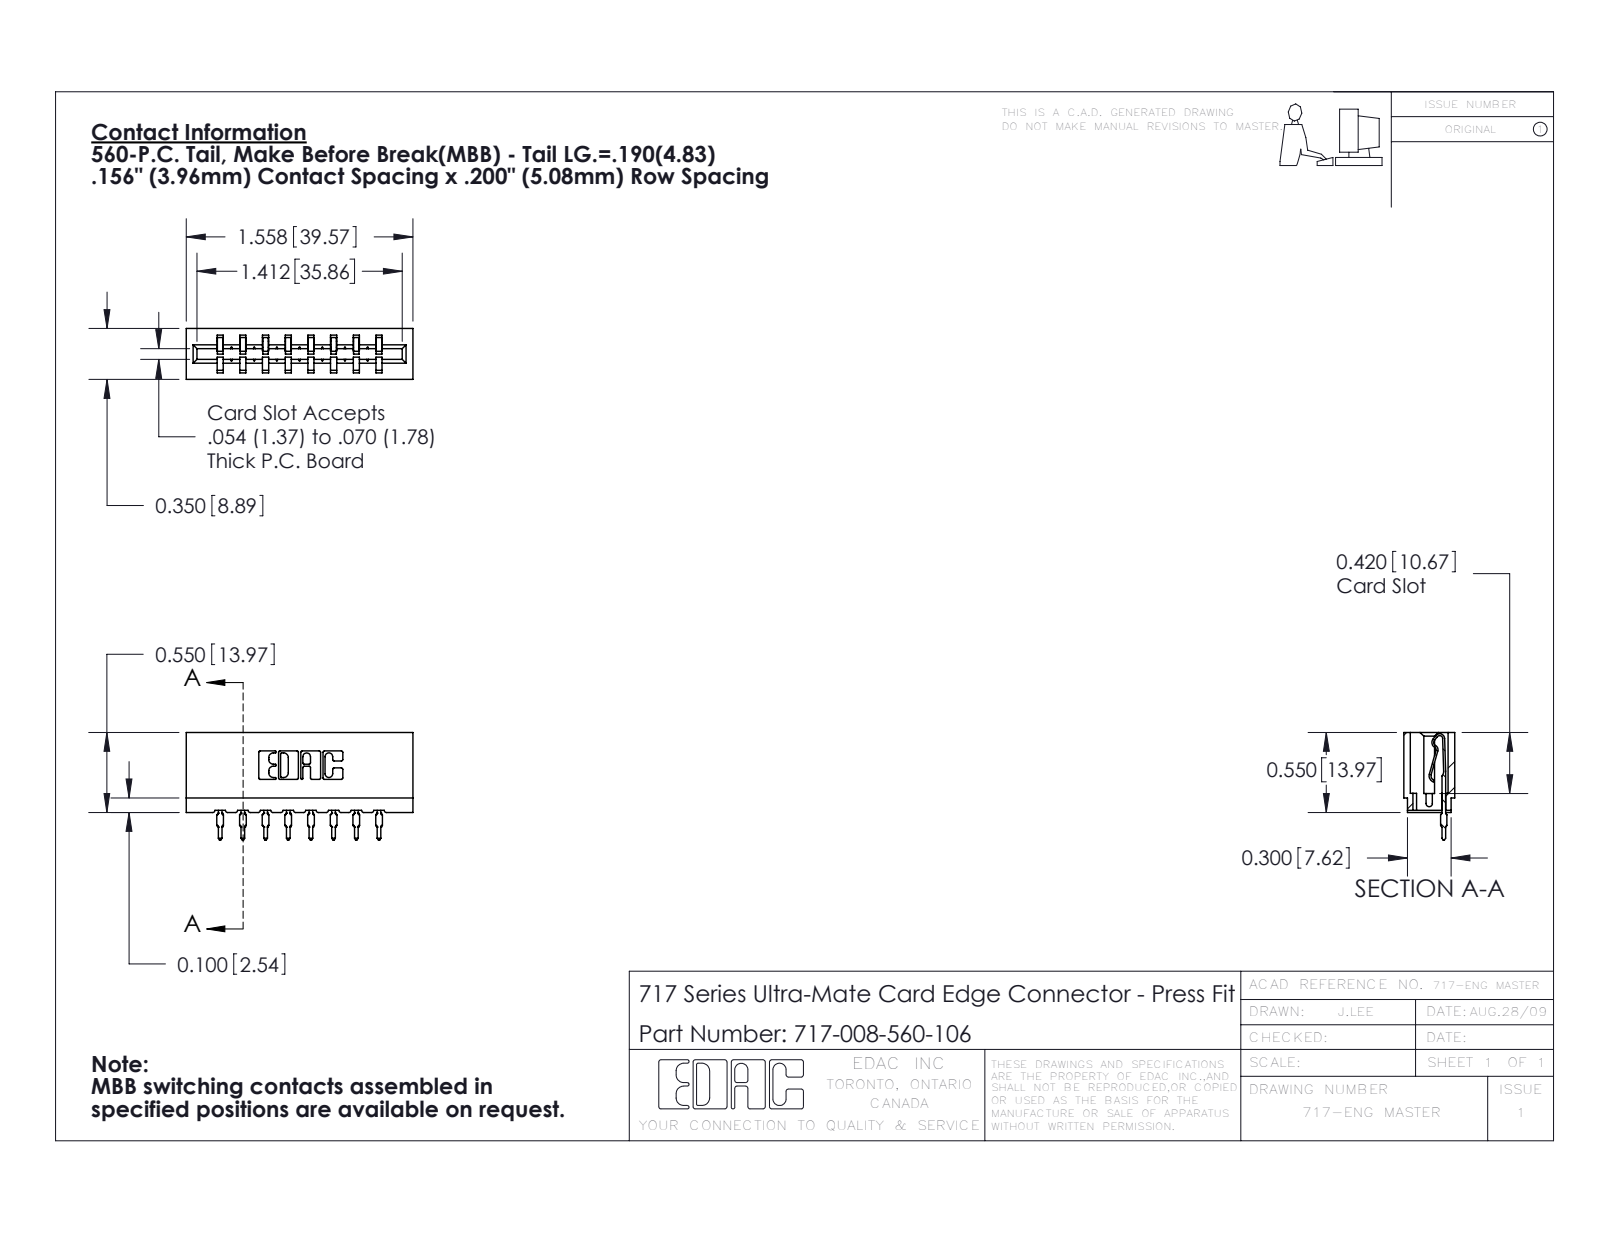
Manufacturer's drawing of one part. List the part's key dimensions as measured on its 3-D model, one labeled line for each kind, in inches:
Part name (STEP PRODUCT): 717 Part_Insulator Option - 06; 745-292-001_560; 717-008-560-106
STEP written by: SolidWorks 2016 (CONFIG_CONTROL_DESIGN)
Units: inches
Bodies: 9 solids, 1070 faces (638 planar, 224 cylindrical, 208 other)
Overall size (bounding box): 1.558 × 0.739 × 0.35
Volume: 0.215 in³ · Surface area: 7.293 in²
Partial cylindrical surfaces — rounded edges, fillets, slot ends (radius × count): R0.01 ×22, R0.015 ×16, R0.021 ×16, R0.007 ×6, R0.031 ×6, R0.005 ×4, R0.011 ×4, R0.026 ×3
Main face-to-face distances: 0.212, 0.156, 0.138, 0.624, 0.468, 0.198, 0.312, 0.35, 0.042, 0.27
